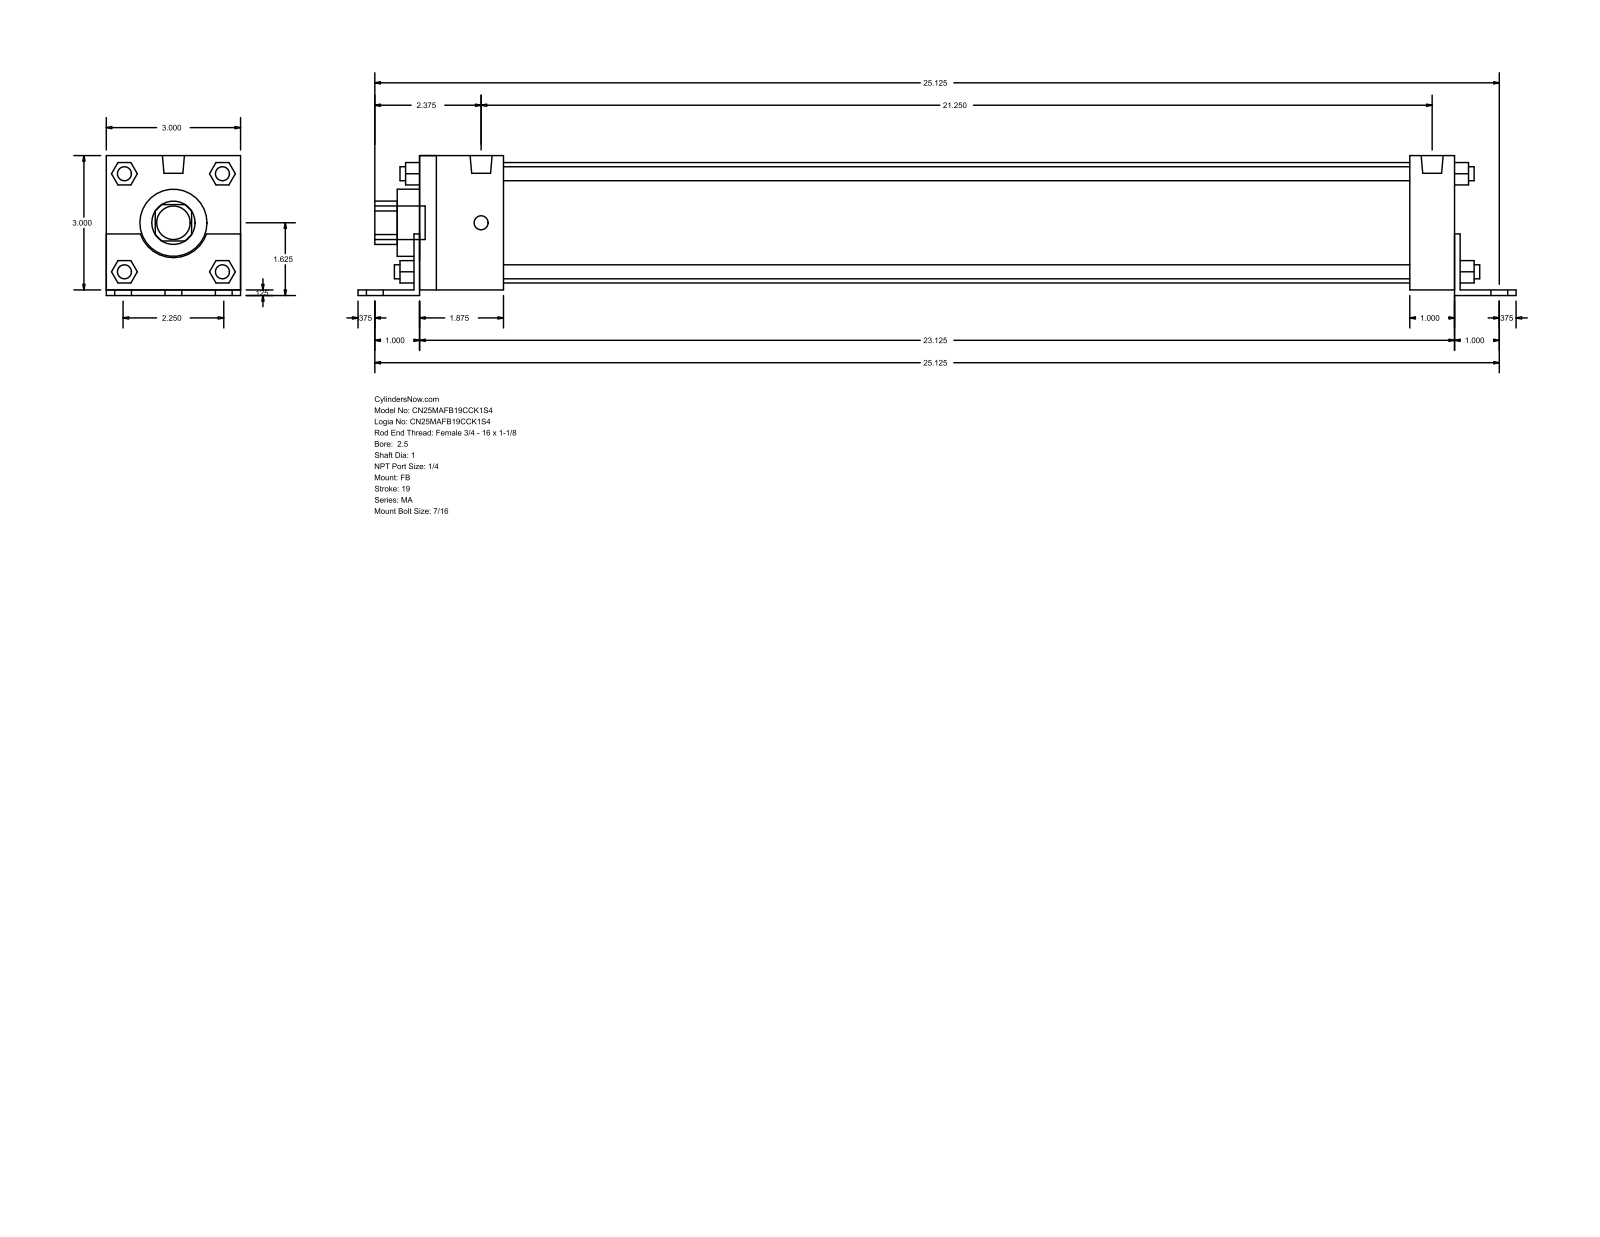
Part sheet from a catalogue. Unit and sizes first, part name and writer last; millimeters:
Units: millimetres
Overall size (bounding box): 657.23 × 79.38 × 76.2
Round holes (diameter × count): ⌀25.4 ×1, ⌀38.1 ×1, ⌀68.33 ×1
Round bosses / shafts (diameter × count): ⌀7.94 ×8, ⌀11.11 ×6, ⌀12.49 ×2, ⌀19.05 ×1
Partial cylindrical surfaces — rounded edges, fillets, slot ends (radius × count): R12.29 ×1, R19.81 ×1
Main face-to-face distances: 76.2, 3.17, 79.37, 587.37, 3.18, 12.7, 590.55, 28.57, 47.63, 539.74
Bodies: 0 solids, 140 faces (105 planar, 35 cylindrical, 0 other)
Part name (STEP PRODUCT): MA_FB__0250_1
STEP written by: GSSL Pune (CONFIG_CONTROL_DESIGN)
